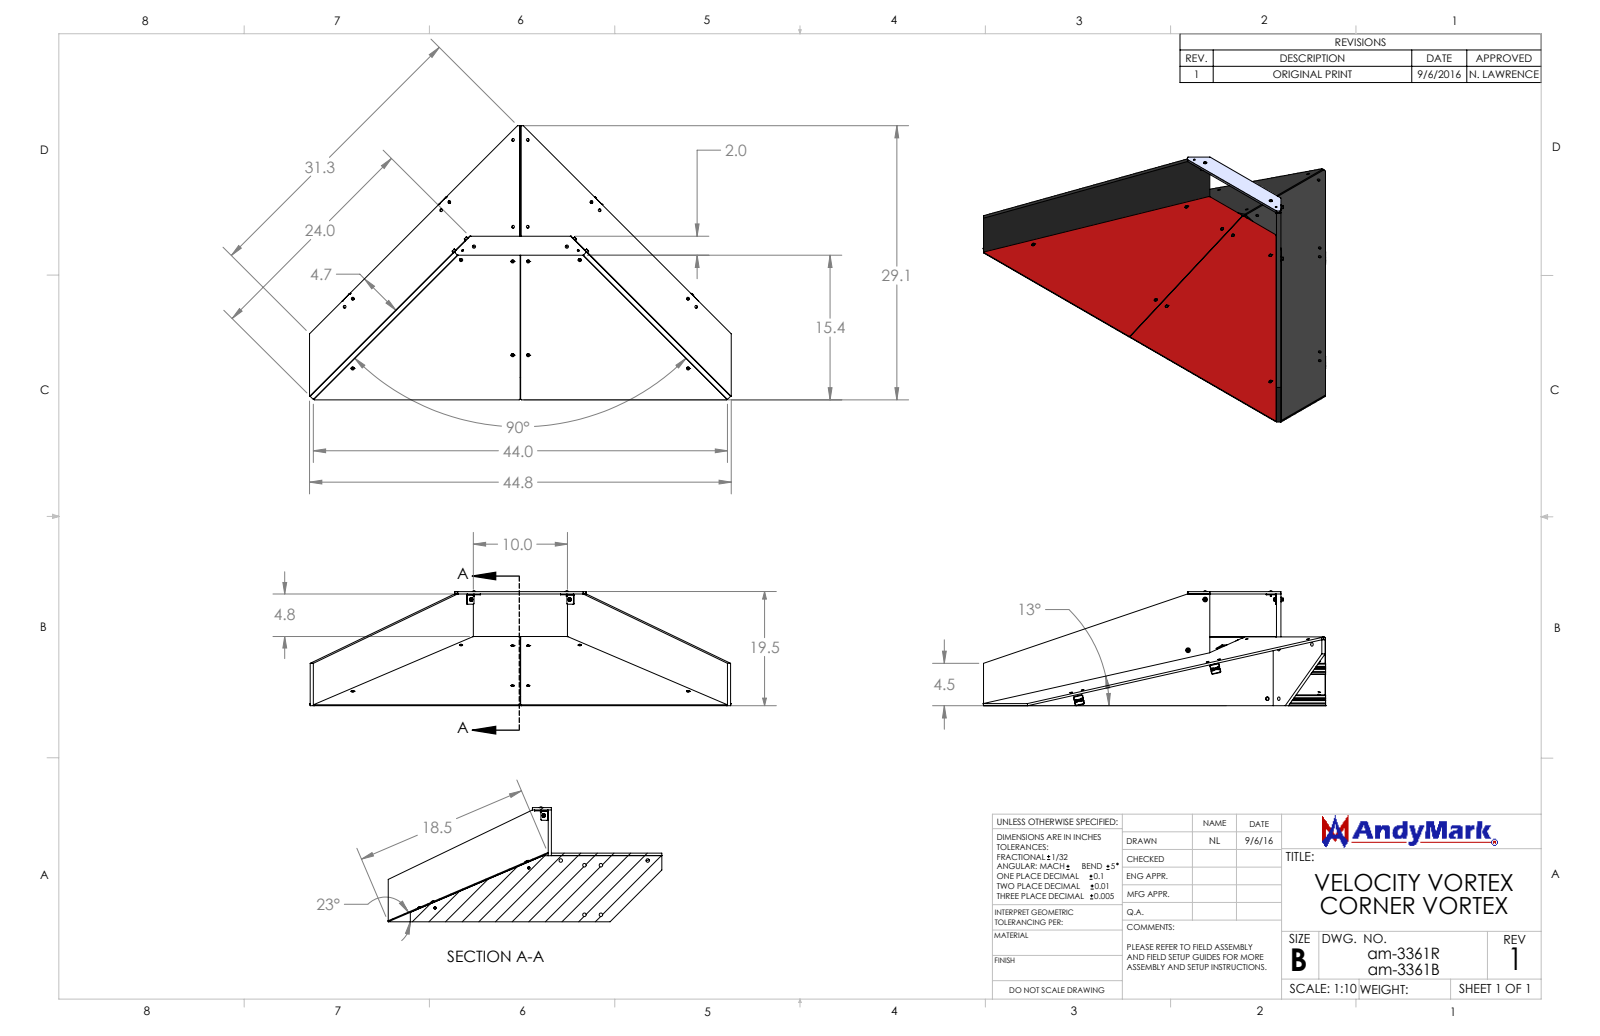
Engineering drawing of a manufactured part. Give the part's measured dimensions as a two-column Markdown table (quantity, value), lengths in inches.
| quantity | value |
| --- | --- |
| part name | CE Goal CrossBar; 0125 x 375Rivet; 10-32 nylock thin nut - Mcm 90633A009_90633A009; CE ramp Surface half (+8 more) |
| STEP written by | SolidWorks 2014 (CONFIG_CONTROL_DESIGN) |
| units | inches |
| bodies | 70 solids, 1798 faces (632 planar, 722 cylindrical, 444 other) |
| overall size | 36.386 × 36.386 × 12.193 |
| volume | 448 in³ |
| surface area | 3 441 in² |
| round holes (diameter × count) | 0.14 × 32, 0.3 × 12, 0.128 × 11, 0.096 × 10, 0.136 × 8, 0.164 × 8, 0.21 × 8, 0.211 × 8, 0.26 × 8, 0.294 × 8, 0.255 × 7, 0.219 × 6 |
| round bosses / shafts (diameter × count) | 0.34 × 10, 0.125 × 10, 0.48 × 8, 0.25 × 8, 0.5 × 6, 0.309 × 6, 0.187 × 6, 0.313 × 2 |
| partial cylindrical surfaces (radius × count) | 0.025 × 48, 0.062 × 37, 0.075 × 32, 0.05 × 16, 0.1 × 16, 0.03 × 10, 0.12 × 10, 0.07 × 8 |
| main face-to-face distances | 0.472, 0.118, 0.236, 0.05, 0.95, 11.874, 12.124, 0.25, 0.048, 0.392 |
| hole center spacings | 10.825, 10.824, 7.137, 0.017, 17, 1.25, 1.652, 5.485 |
